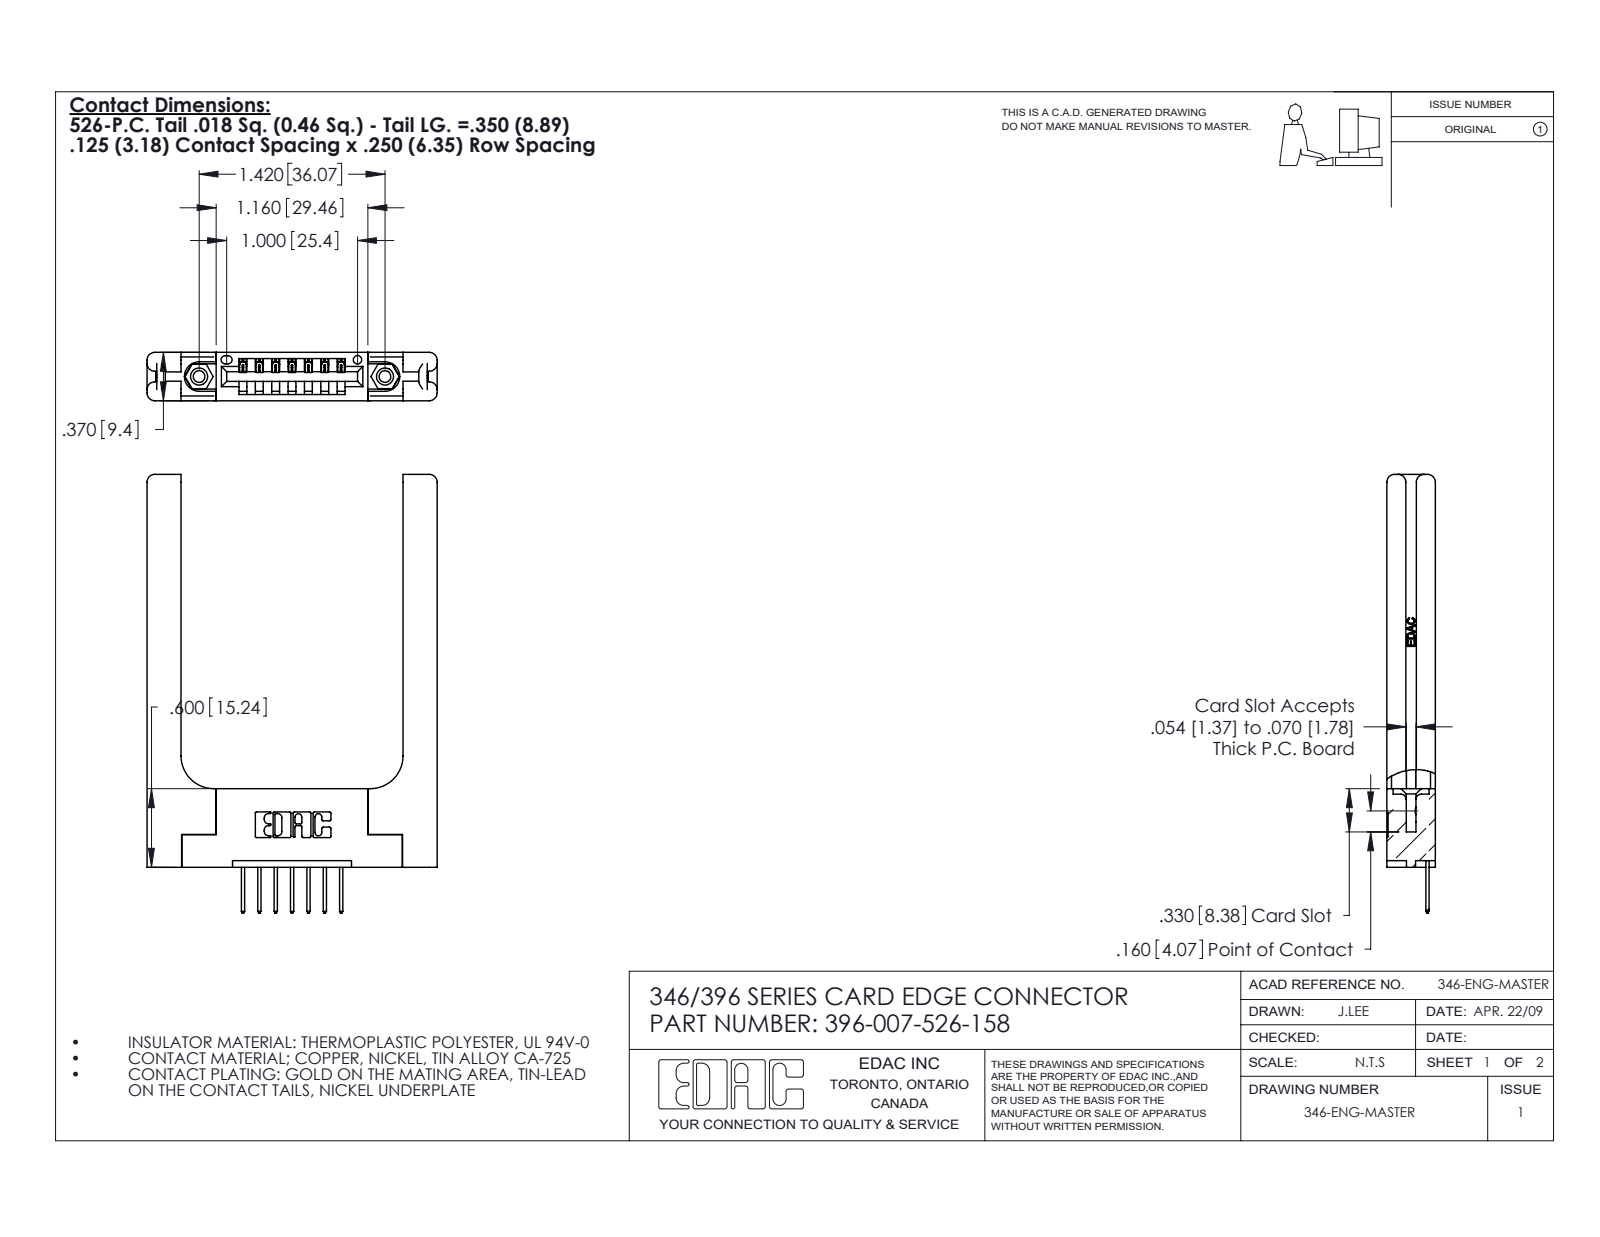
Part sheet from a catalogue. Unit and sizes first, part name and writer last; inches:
Units: inches
Overall size (bounding box): 3.35 × 2.216 × 0.37
Round holes (diameter × count): ⌀0.089 ×2, ⌀0.125 ×2, ⌀0.156 ×2, ⌀0.064 ×1
Round bosses / shafts (diameter × count): ⌀0.155 ×2
Partial cylindrical surfaces — rounded edges, fillets, slot ends (radius × count): R0.01 ×22, R0.06 ×16, R0.006 ×14, R0.01 ×14, R0.007 ×6, R0.031 ×6, R0.026 ×3, R0.03 ×2
Main face-to-face distances: 0.37, 0.15, 0.22, 0.072, 0.148, 0.25, 1.696, 0.102, 0.048, 0.322
Hole centre spacings: 0.246, 1.217, 1.42
Volume: 0.771 in³ · Surface area: 17.39 in²
Bodies: 12 solids, 798 faces (518 planar, 220 cylindrical, 60 other)
Part name (STEP PRODUCT): 346 Part_Flush Mounting Lugs - 0.156 Dia-TH; 345-292-001_345-293-126; 346-220-058_345-220-058; 396-007-526-158 (+1 more)
STEP written by: SolidWorks 2020 (CONFIG_CONTROL_DESIGN)
